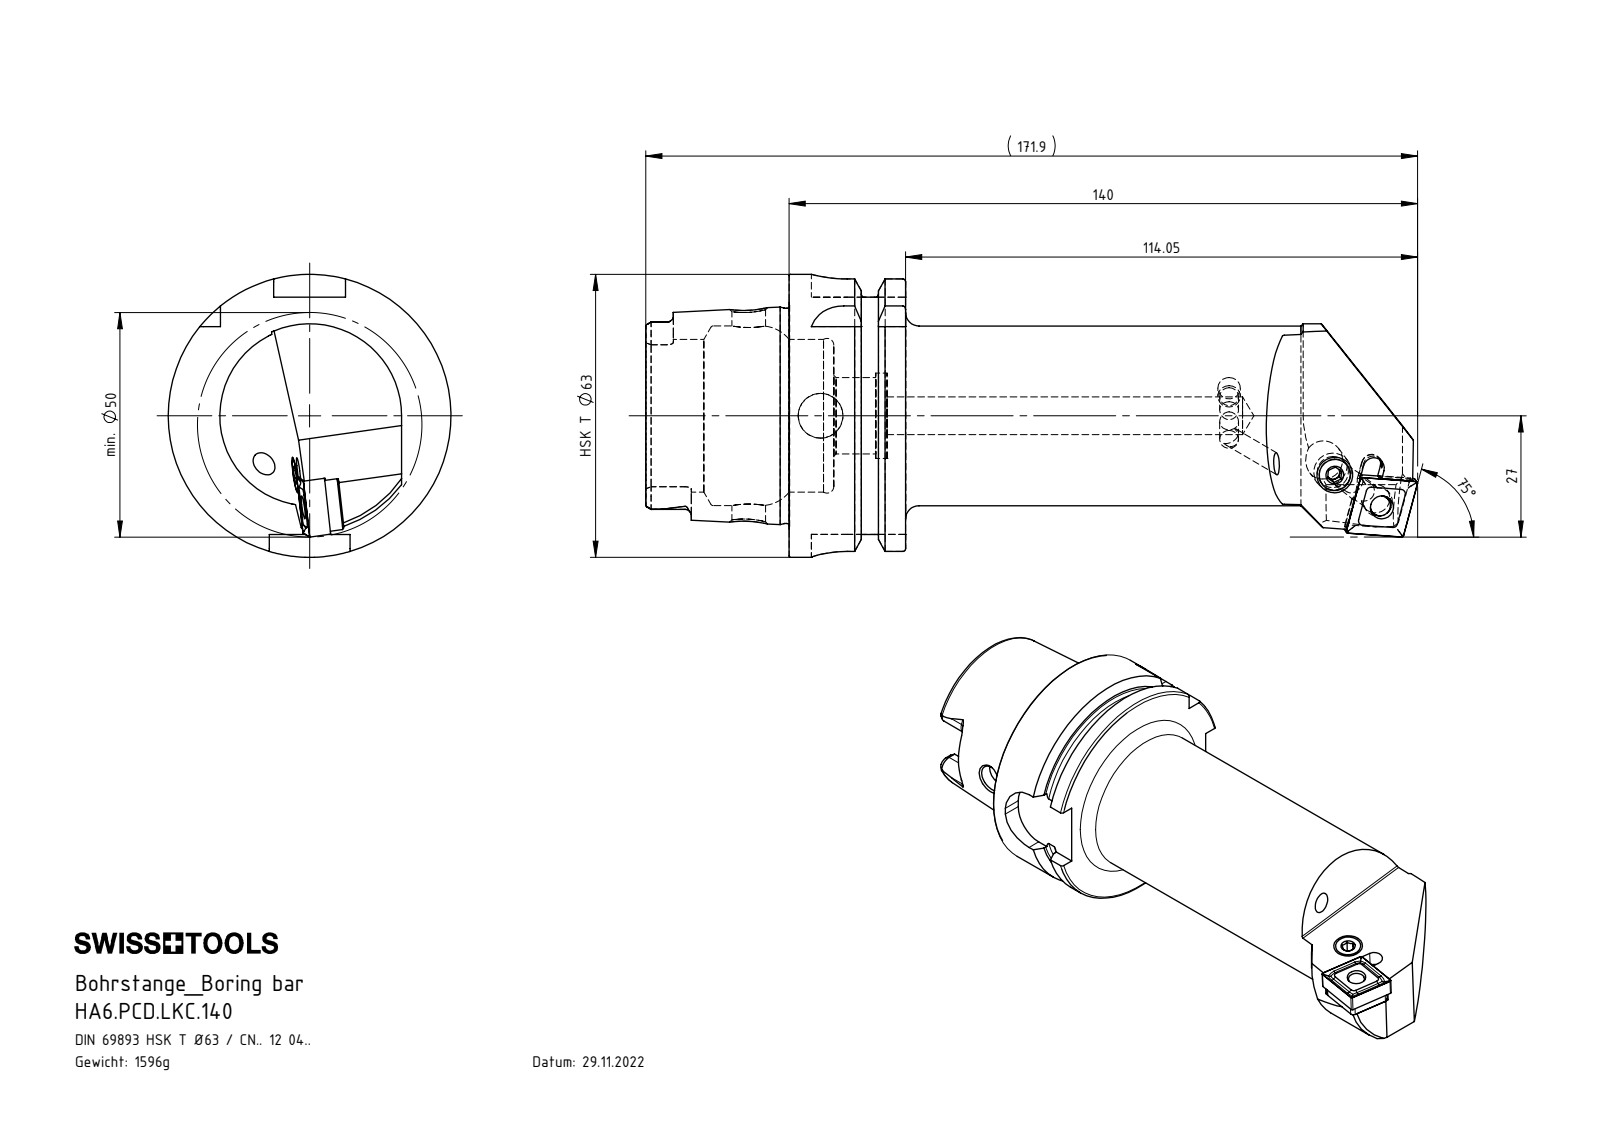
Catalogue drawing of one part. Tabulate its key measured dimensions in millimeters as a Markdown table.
| quantity | value |
| --- | --- |
| part name | HA6.PCD.LKC.140; WCD-ER4.101.017_A; WCD; WCD-ER3.101.000_A (+4 more) |
| STEP written by | SolidWorks 2017 (AUTOMOTIVE_DESIGN) |
| units | millimeters |
| bodies | 7 solids, 364 faces (115 planar, 103 cylindrical, 146 other) |
| overall size | 171.9 × 63 × 63 |
| volume | 202 478 mm³ |
| surface area | 40 870 mm² |
| round holes (diameter × count) | 4.2 × 2, 8.4 × 2, 4 × 1, 5 × 1, 5.16 × 1, 6.4 × 1, 7 × 1, 7.5 × 1, 10 × 1, 17 × 1, 19 × 1, 34 × 1 |
| round bosses / shafts (diameter × count) | 63 × 1, 54.95 × 1, 47.94 × 1, 8 × 1, 7.9 × 1, 6.4 × 1, 5 × 1, 4.5 × 1 |
| partial cylindrical surfaces (radius × count) | 1.4 × 6, 0.4 × 4, 1 × 4, 8 × 4, 2.5 × 2, 2.82 × 2, 2.88 × 2, 0.5 × 1 |
| main face-to-face distances | 25.95, 16, 9.95, 31.9, 41.85, 57.85, 52.8, 21.8, 11.85, 4.48 |
| hole center spacings | 12.79, 12.84 |
